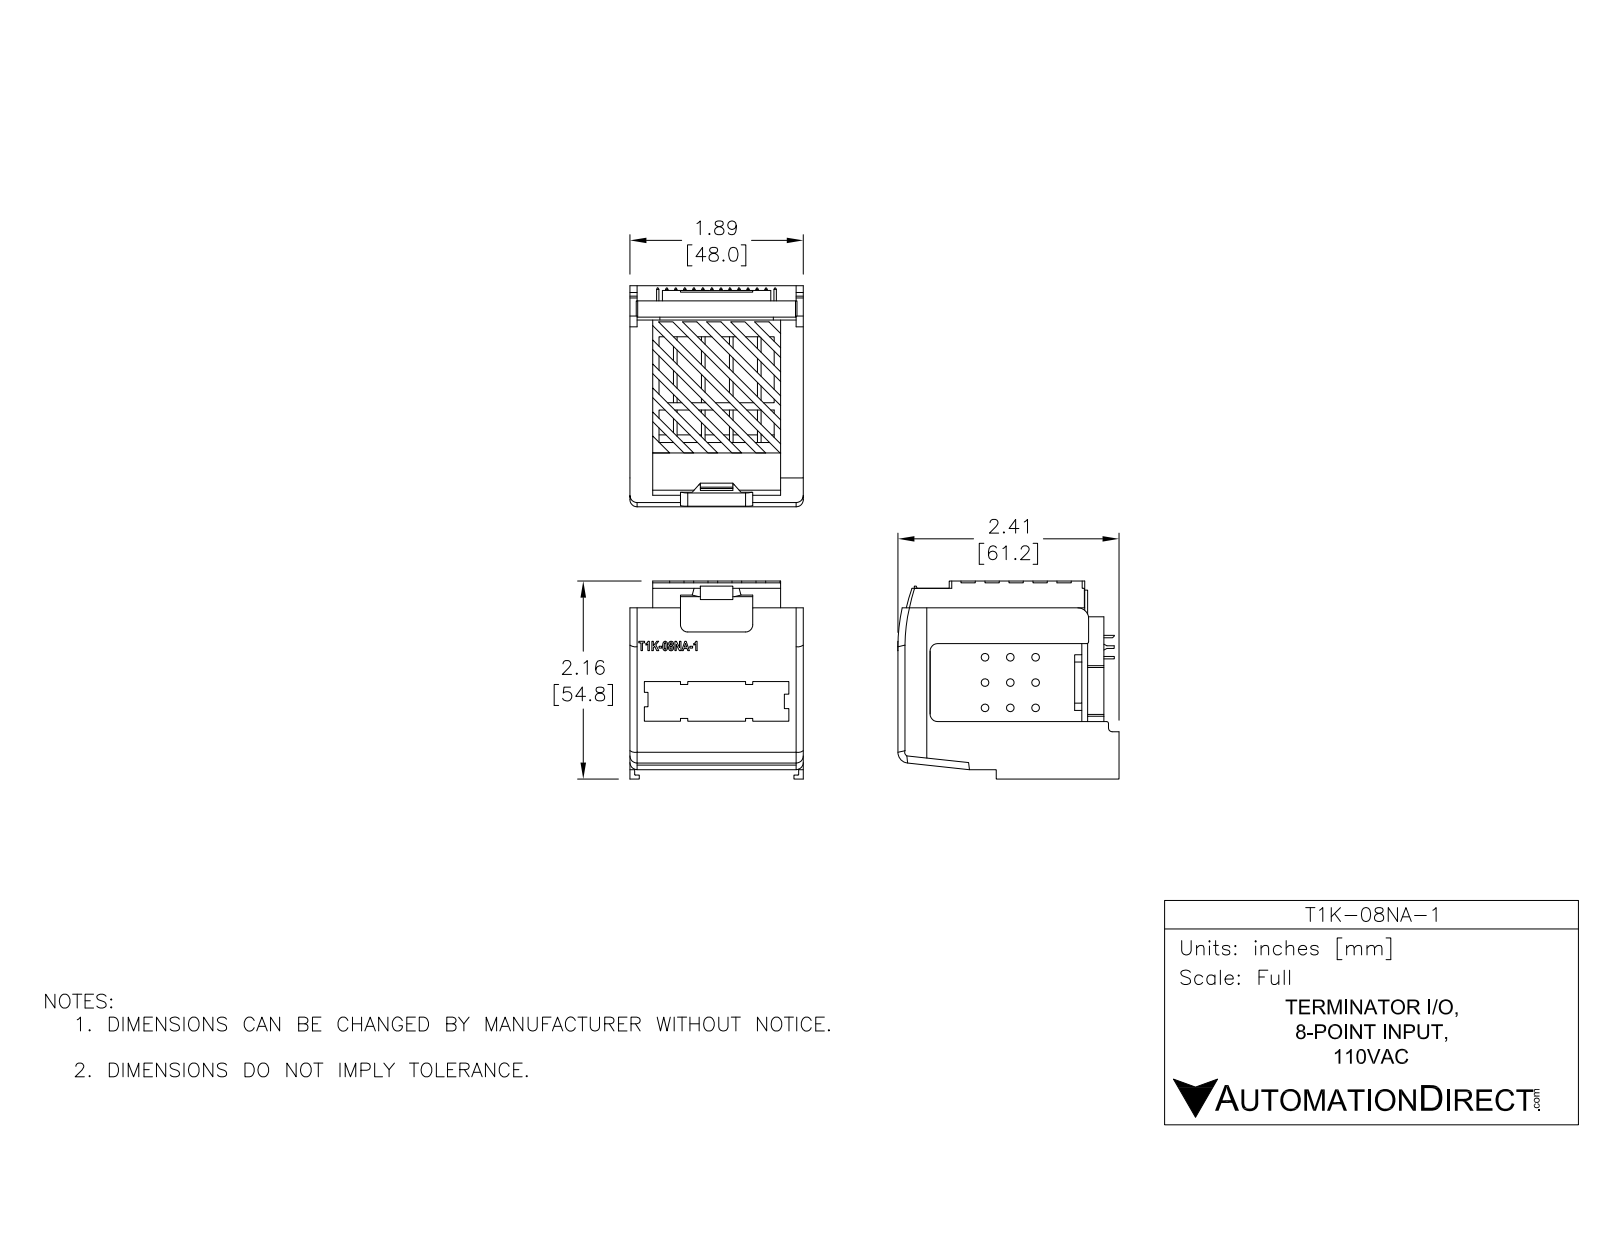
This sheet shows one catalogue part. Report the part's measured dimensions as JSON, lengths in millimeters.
{"part_name": "T1K-08NNA-1", "step_written_by": "SolidWorks 2013 (AUTOMOTIVE_DESIGN)", "units": "millimeters", "bodies": {"solids": 1, "faces": 554, "planar": 425, "cylindrical": 101, "other": 28}, "overall_size": [65.1, 61.36, 47.6], "volume_mm3": 30279, "surface_area_mm2": 35941, "round_holes": [[3, 8]], "round_bosses_or_shafts": [[0.7, 28]], "partial_cylinders_radius": [[3.5, 10], [1, 5], [0.25, 3], [0.55, 3], [1.5, 2], [8, 1], [10, 1], [18, 1]], "face_to_face_distances": [2, 45.6, 47.6, 43.6, 55.35, 49.9, 6.55, 39.05, 59.8, 9.9], "hole_center_spacings": [5.2, 10.4, 15.6, 20.8, 26, 31.2, 36.4]}
